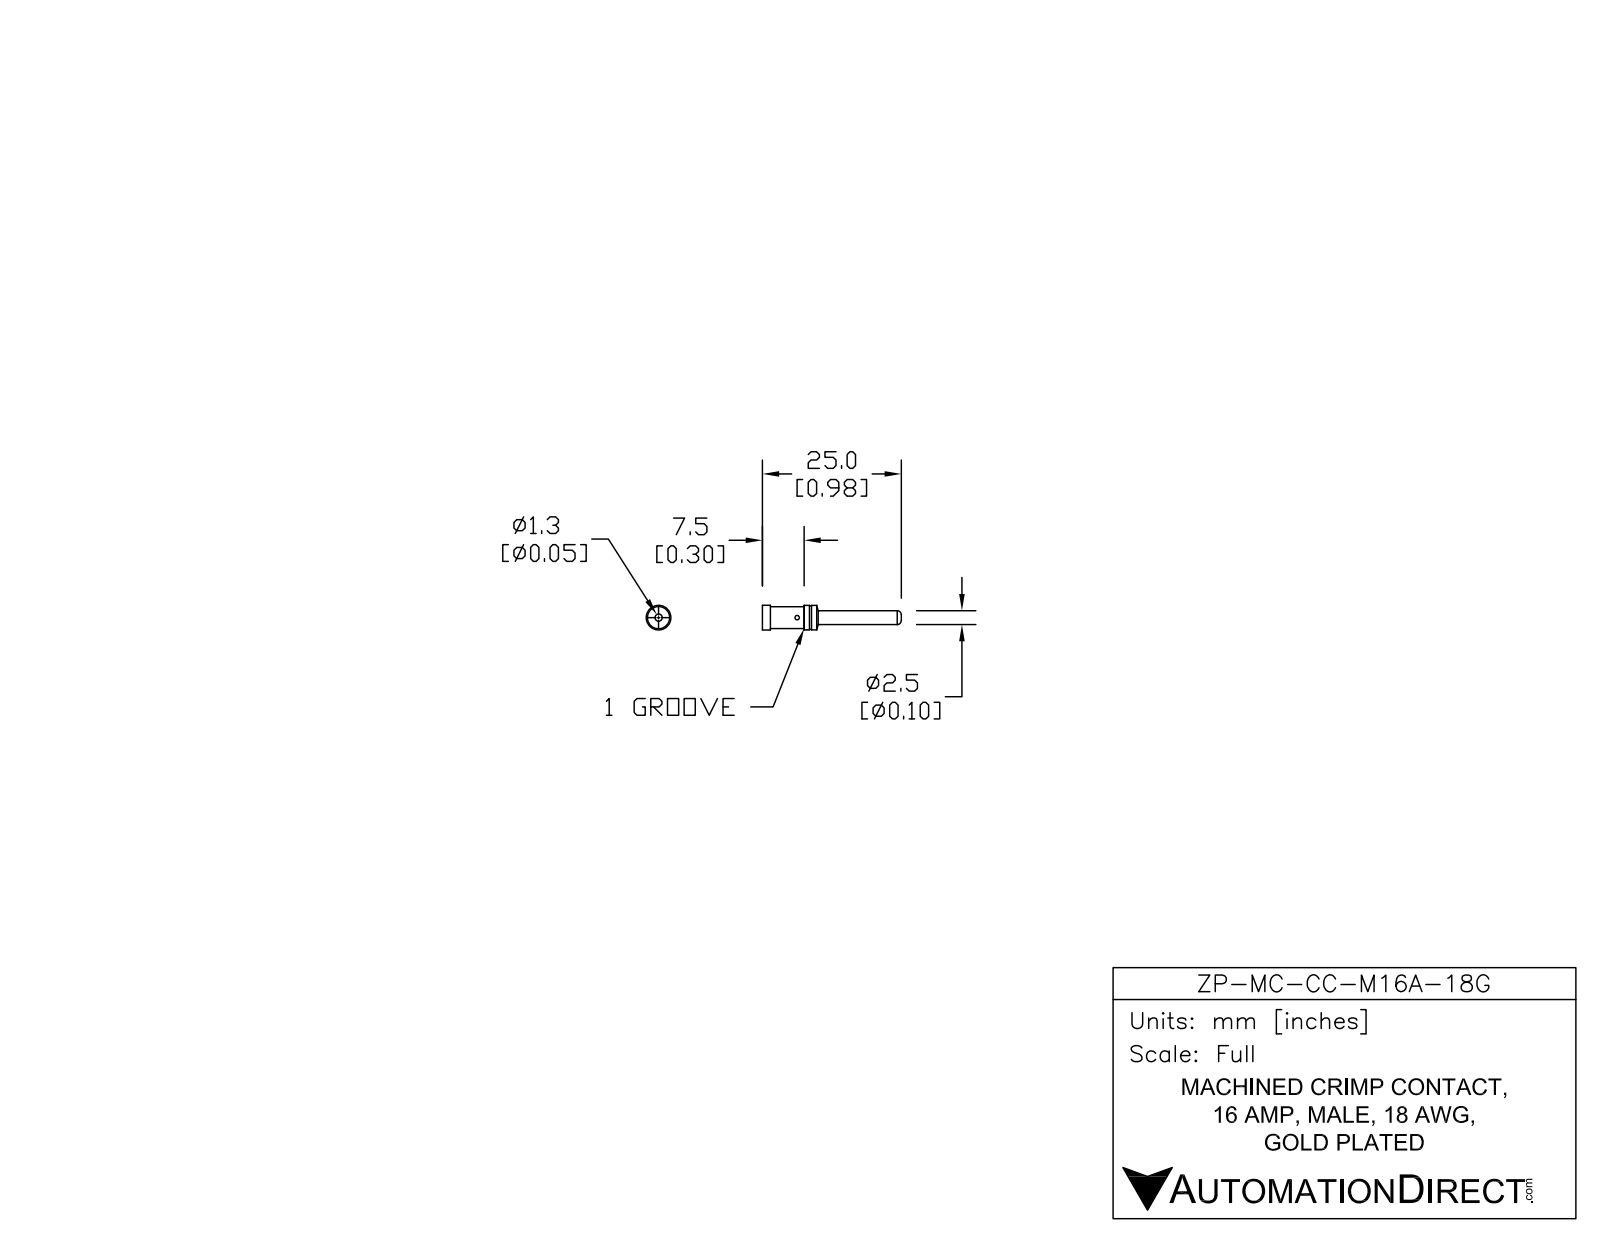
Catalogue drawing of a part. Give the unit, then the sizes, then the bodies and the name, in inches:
Units: inches
Overall size (bounding box): 0.984 × 0.175 × 0.175
Round holes (diameter × count): ⌀0.031 ×1, ⌀0.051 ×1
Round bosses / shafts (diameter × count): ⌀0.175 ×1, ⌀0.16 ×1, ⌀0.106 ×1, ⌀0.098 ×1
Main face-to-face distances: 0.295, 0.035, 0.33, 0.019, 0.054, 0.349, 0.025, 0.044, 0.079, 0.374
Volume: 0.009 in³ · Surface area: 0.484 in²
Bodies: 1 solid, 31 faces (7 planar, 16 cylindrical, 8 other)
Part name (STEP PRODUCT): ZP-MC-CC-M16A-18G
STEP written by: SolidWorks 2014 (AUTOMOTIVE_DESIGN)
